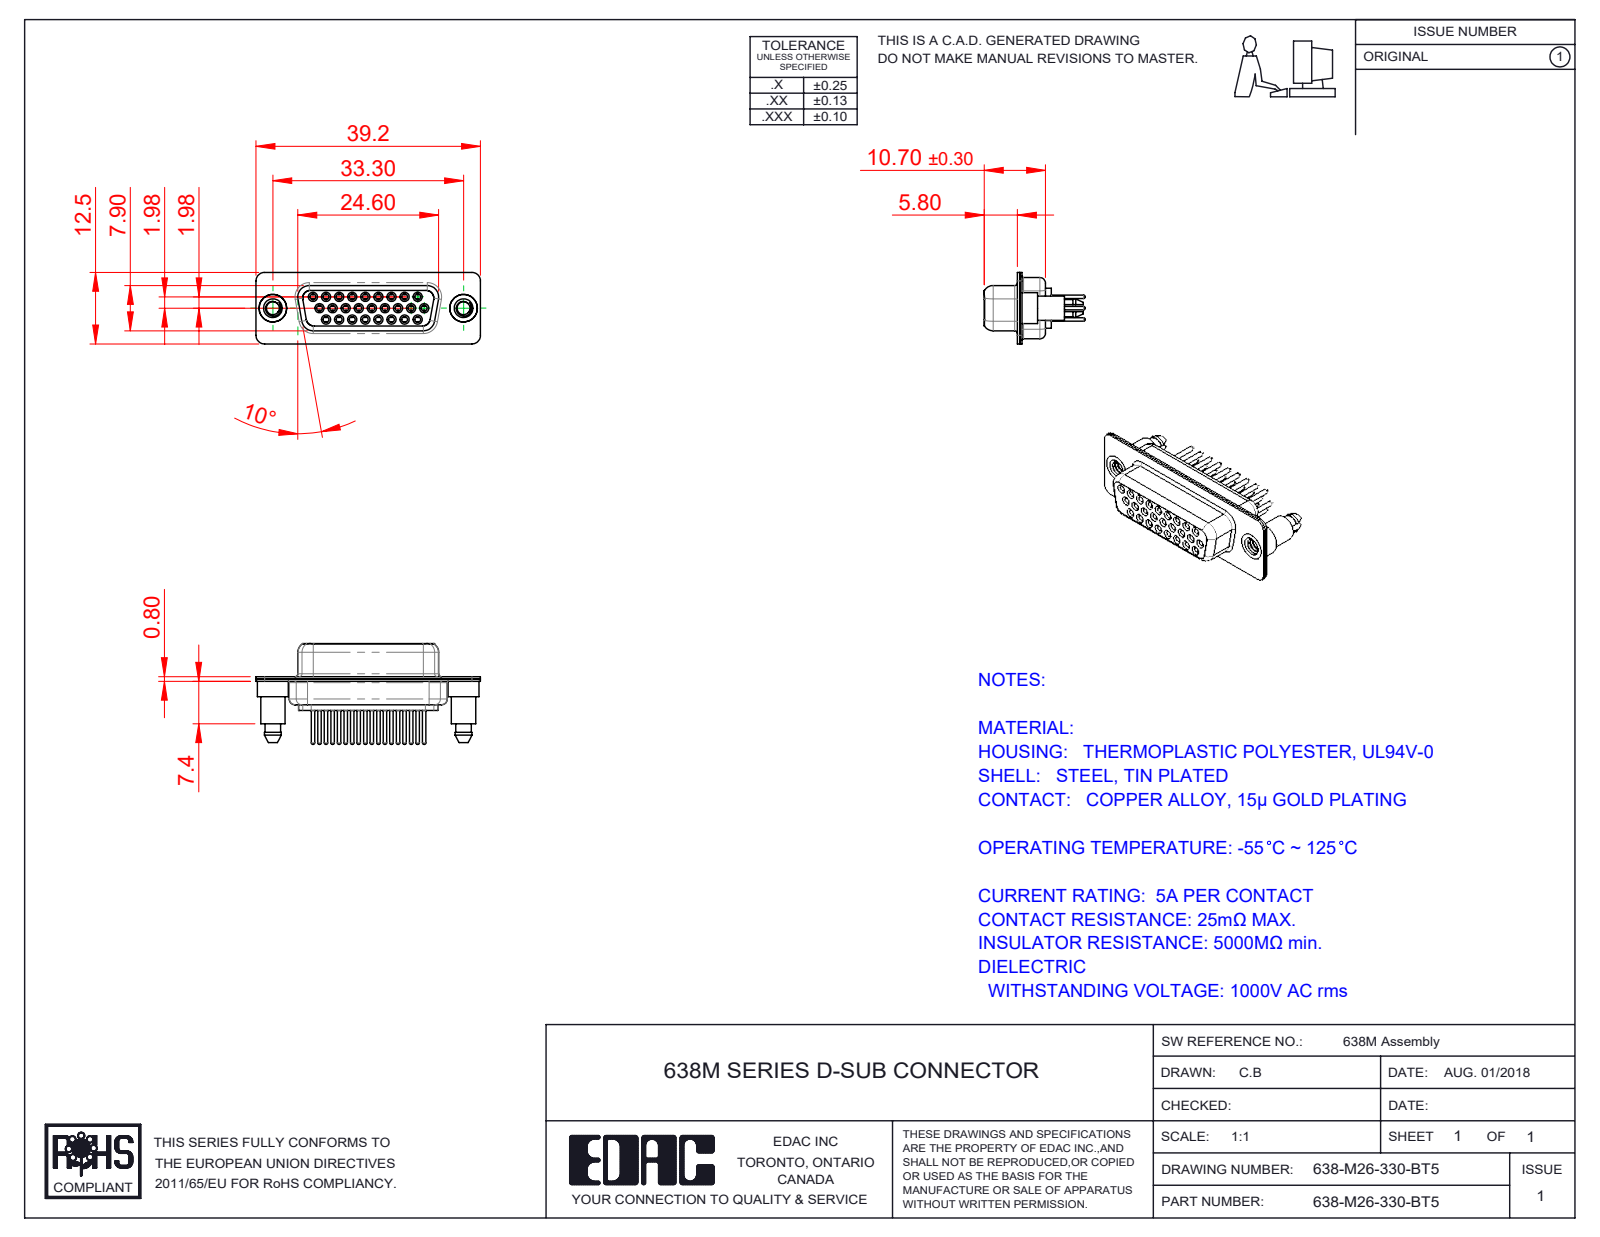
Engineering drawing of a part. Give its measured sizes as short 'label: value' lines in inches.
name: 638M Shell Rear_26 Contacts; 638M Contact Row 1_30; 638M Contact Row 2_30; 638M 4-40 Threaded Boardlock (+4 more)
written by: SolidWorks 2020 (CONFIG_CONTROL_DESIGN)
unit: in
bodies: 31 solids, 1759 faces (473 planar, 663 cylindrical, 623 other)
size: 1.543 × 0.693 × 0.492
volume: 0.152 in³; area: 12.7 in²
holes: 26× ⌀0.039, 26× ⌀0.043, 26× ⌀0.067, 26× ⌀0.071, 26× ⌀0.079, 2× ⌀0.089, 2× ⌀0.157, 2× ⌀0.189
bosses: 26× ⌀0.087, 26× ⌀0.063, 26× ⌀0.059, 26× ⌀0.024, 2× ⌀0.213, 2× ⌀0.193, 2× ⌀0.167
rounds: 18× R0.059, 12× R0.079, 10× R0.063, 8× R0.053, 4× R0.01, 4× R0.02, 4× R0.024, 4× R0.026
face distances: 0.016, 0.055, 0.018, 0.333, 0.35, 0.039, 0.071, 0.244, 0.278, 0.073
hole spacings: 0.156, 0.09, 0.18, 0.238, 0.09, 0.324, 0.27, 0.238
